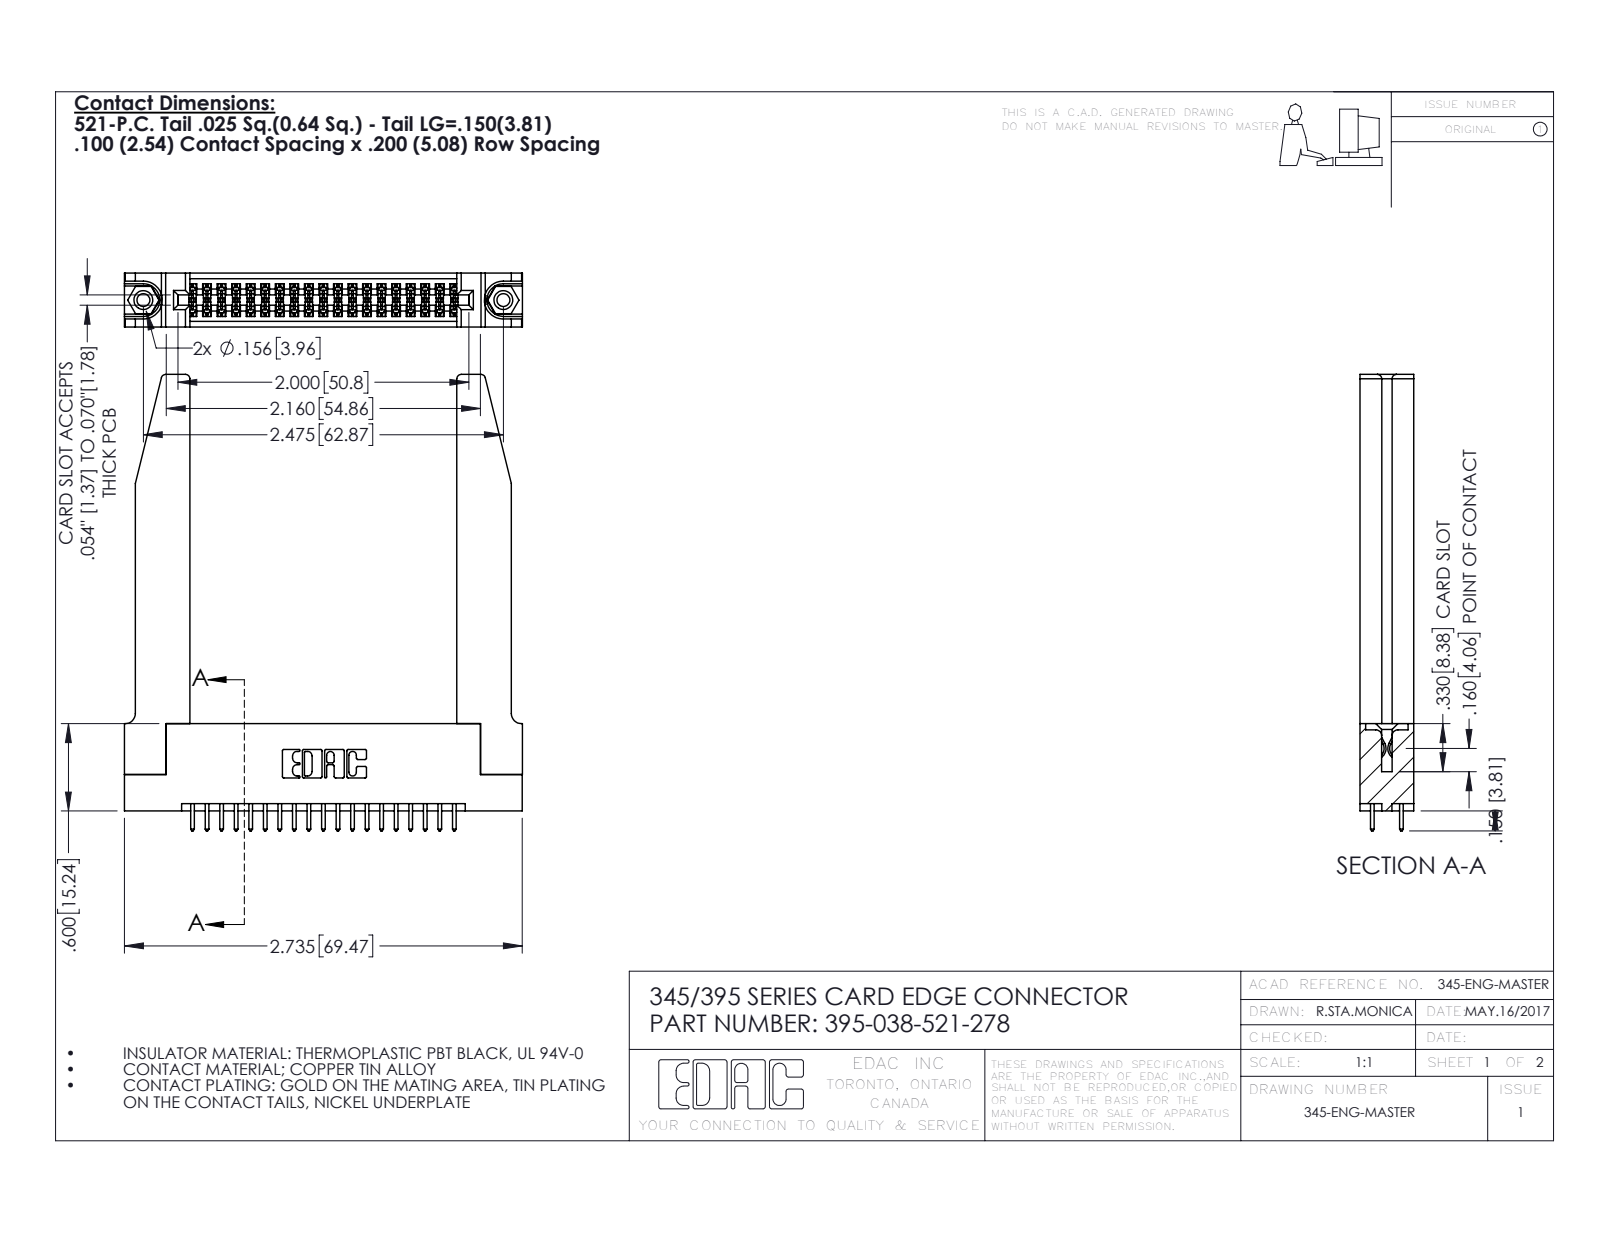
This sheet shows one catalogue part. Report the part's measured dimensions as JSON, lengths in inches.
{"part_name": "395-038-521-278; 345 Part_Flush Mounting Lugs - 0.156 Dia-TH; 345-292-001_345-293-121; 345-250-001_345-250-001-102 (+1 more)", "step_written_by": "SolidWorks 2016 (CONFIG_CONTROL_DESIGN)", "units": "inches", "bodies": {"solids": 43, "faces": 2260, "planar": 1476, "cylindrical": 732, "other": 52}, "overall_size": [3.137, 2.736, 0.37], "volume_in3": 0.872, "surface_area_in2": 24.7, "round_holes": [[0.089, 2], [0.125, 2], [0.156, 2], [0.064, 1]], "round_bosses_or_shafts": [[0.155, 2]], "partial_cylinders_radius": [[0.006, 57], [0.01, 38], [0.01, 22], [0.03, 8], [0.007, 6], [0.031, 6], [0.026, 3], [0.014, 2]], "face_to_face_distances": [0.37, 0.072, 0.298, 0.2, 0.098, 0.272, 0.025, 0.225, 0.148, 0.15], "hole_center_spacings": [0.27, 2.241, 2.475]}
